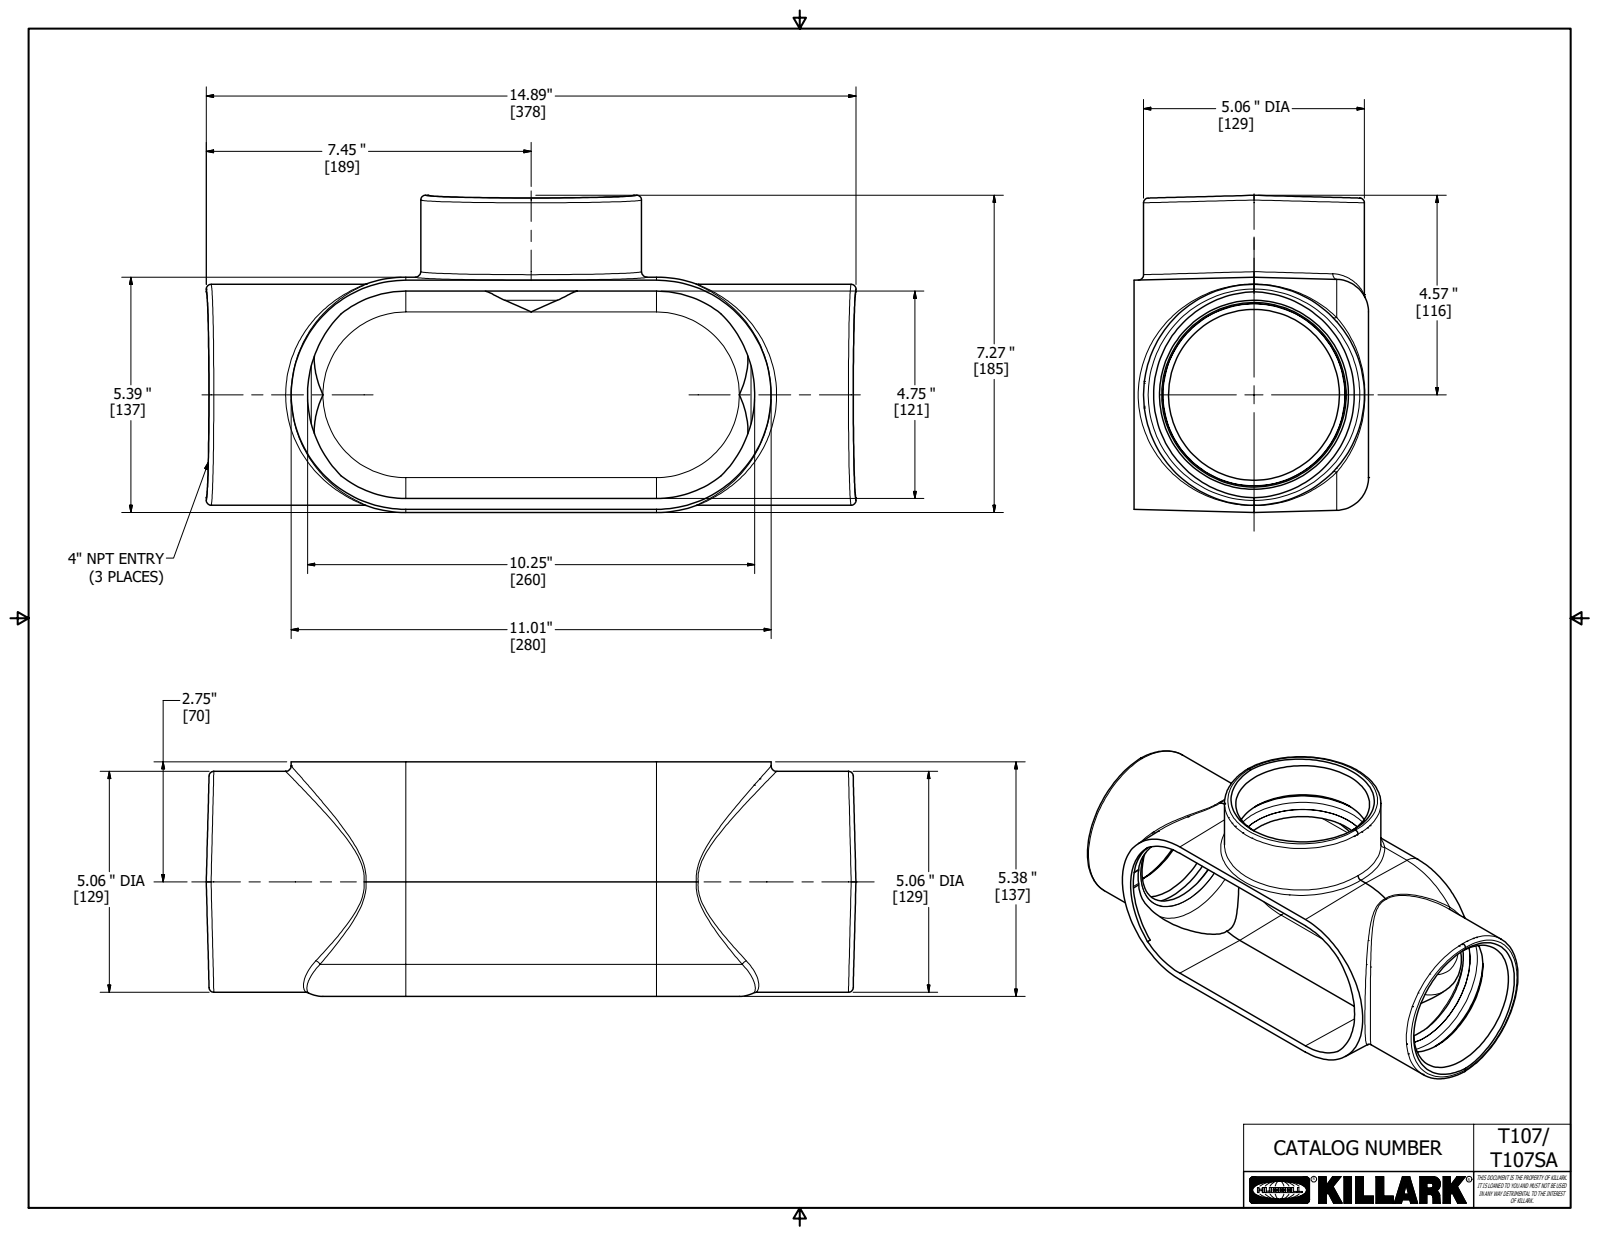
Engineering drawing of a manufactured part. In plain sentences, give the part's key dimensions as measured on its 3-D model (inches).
The part is named "17745". Its 3-D file was written by "Autodesk Inventor 2018 (AUTOMOTIVE_DESIGN)". It is 1 solid with 114 faces: 34 planar, 22 cylindrical and 58 other. Overall it measures 14.894 by 7.269 by 5.375 inches. Its volume is 68.9 cubic inches and its surface area 506.8 square inches. Round holes: 2 of diameter 4.511, 1 of diameter 4.75. Round bosses or shafts: 2 of diameter 5.062. Partial cylindrical surfaces (rounded edges, fillets, slot ends): 4 of radius 0.05, 4 of radius 0.125, 2 of radius 0.5, 2 of radius 0.75, 1 of radius 2.375. The main face-to-face distances are 0.25, 5.144, 4.894, 5.375, 5.125, 5.394, 0.031, 0.219, 5.344, 14.894.
